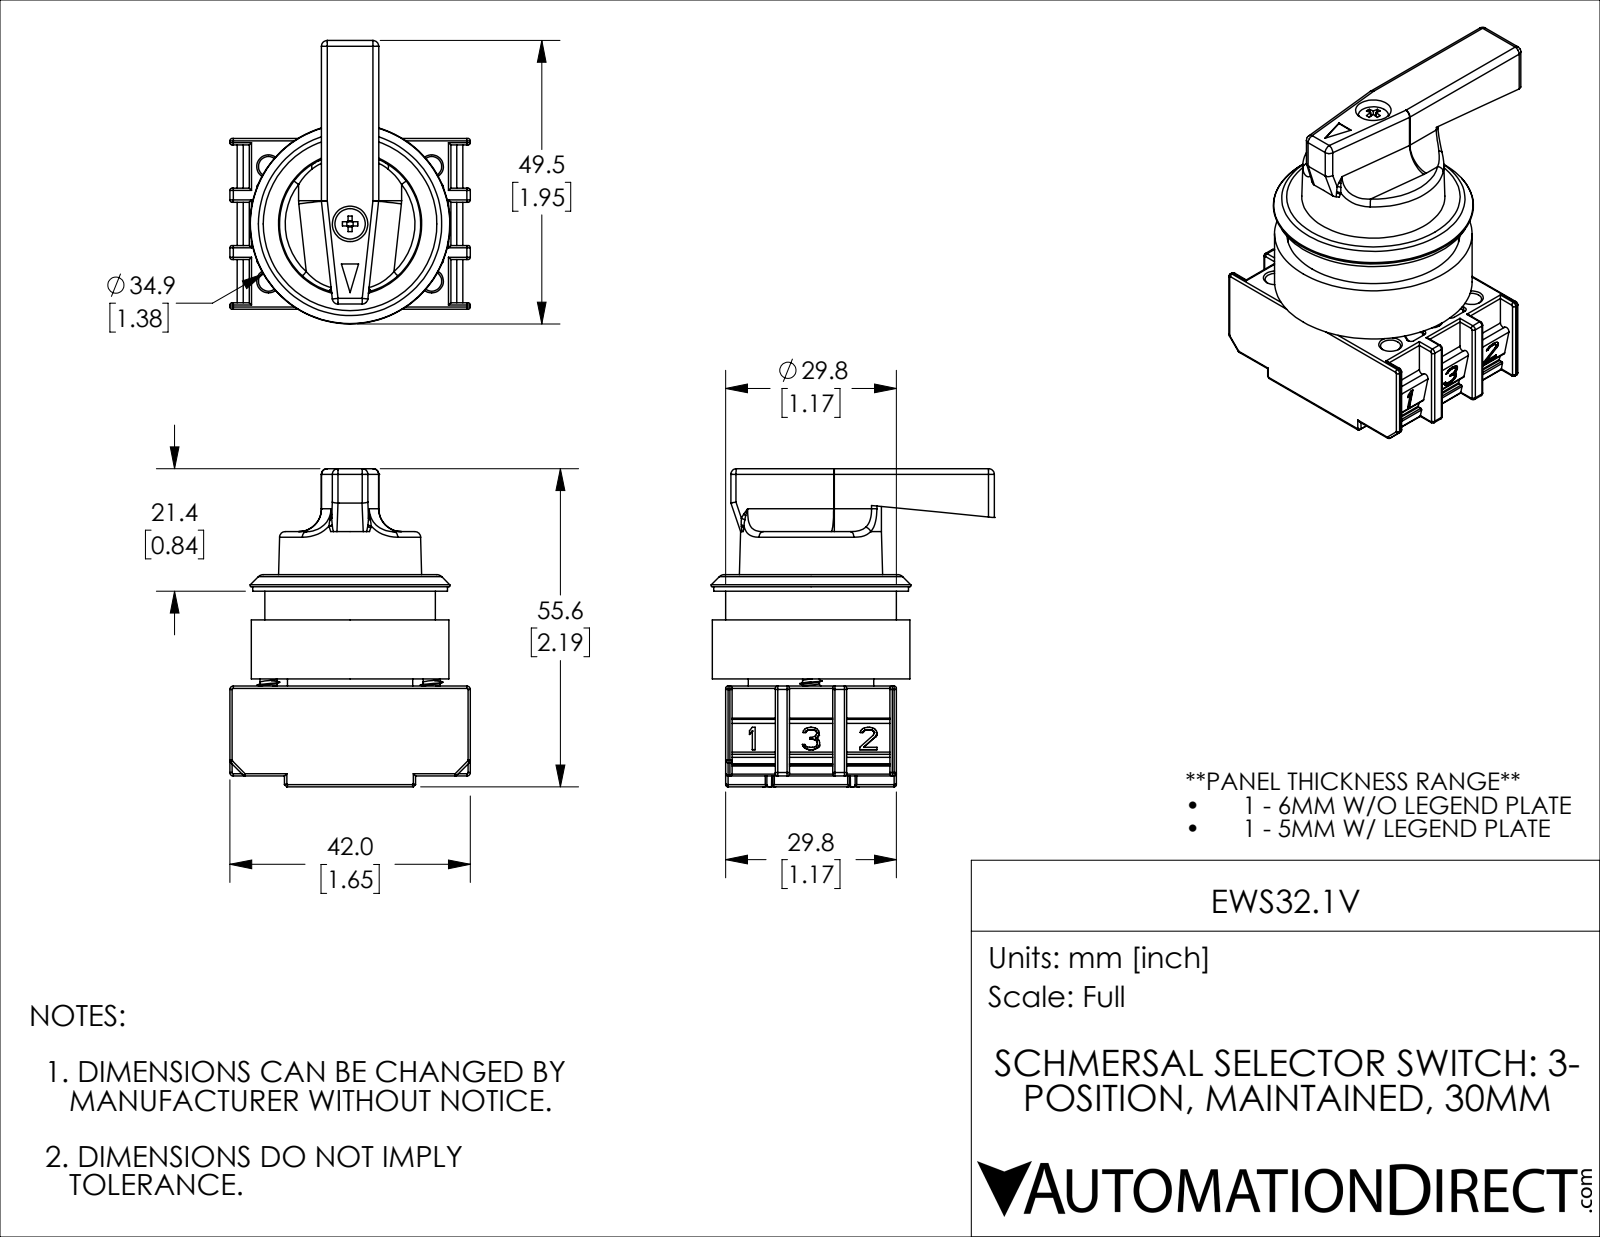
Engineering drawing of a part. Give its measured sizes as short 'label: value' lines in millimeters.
name: EWS32.1V
written by: SolidWorks 2019 (CONFIG_CONTROL_DESIGN)
unit: mm
bodies: 5 solids, 1738 faces (639 planar, 598 cylindrical, 501 other)
size: 55.55 × 49.47 × 42
volume: 29 601 mm³; area: 26 700 mm²
holes: 6× ⌀3.5, 6× ⌀5.15, 4× ⌀2, 4× ⌀5, 2× ⌀1.65, 2× ⌀1.95, 1× ⌀6.2, 1× ⌀9.15, 1× ⌀11, 1× ⌀14, 1× ⌀19, 1× ⌀22
bosses: 4× ⌀4.8, 2× ⌀2.93, 1× ⌀34.5, 1× ⌀34, 1× ⌀29.8, 1× ⌀25.5, 1× ⌀21.9, 1× ⌀18.5
rounds: 120× R0.4, 48× R0.3, 40× R1, 28× R0.2, 14× R0.5, 8× R0.6, 6× R0.8, 4× R4
face distances: 16.1, 17.35, 18.85, 29.8, 2.1, 18.2, 10, 18.3, 37.05, 34.95
hole spacings: 14.33, 3.03, 4.24, 6, 6.26, 7.07, 9.01, 10
